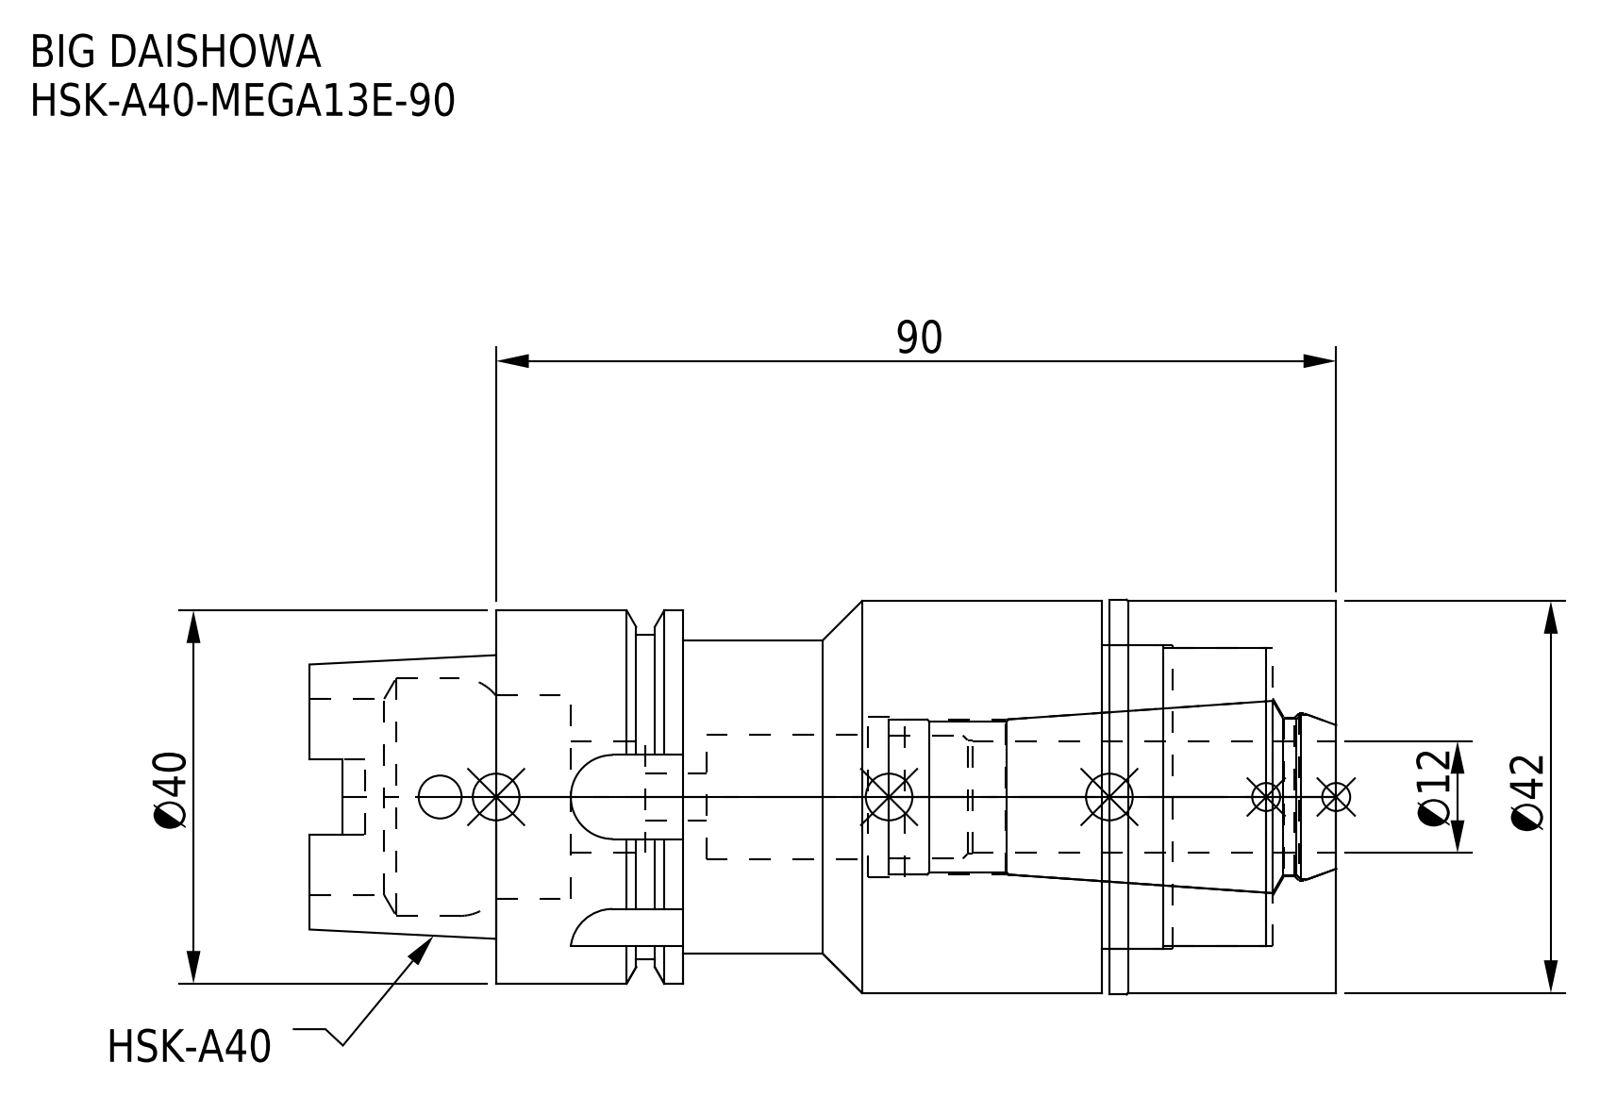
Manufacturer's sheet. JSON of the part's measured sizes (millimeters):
{"part_name": "HSK-A40-MEGA13E-90; HA40ME13090-120_ASM.stp; HSK-A40-MEGA13E-90_1.stp; MEN13_1.stp (+3 more)", "step_written_by": "SolidWorks 2019 (CONFIG_CONTROL_DESIGN)", "units": "millimeters", "bodies": {"solids": 2, "faces": 129, "planar": 45, "cylindrical": 58, "other": 26}, "overall_size": [110, 42.3, 42.3], "volume_mm3": 96876, "surface_area_mm2": 28285, "round_holes": [[4.6, 1], [5, 1], [12, 1], [13.3, 1], [16.6, 1], [17, 1], [17.2, 1], [17.9, 1], [21, 1], [21.8, 1], [25.5, 1], [32, 1]], "round_bosses_or_shafts": [[42.3, 1], [42, 1], [40, 1], [34.8, 1], [33.6, 1]], "partial_cylinders_radius": [[1.88, 4], [4.5, 4]], "face_to_face_distances": [25.1, 24.3, 7.5, 0.8, 90, 65.7, 64.9, 17.5, 6.8, 20]}
